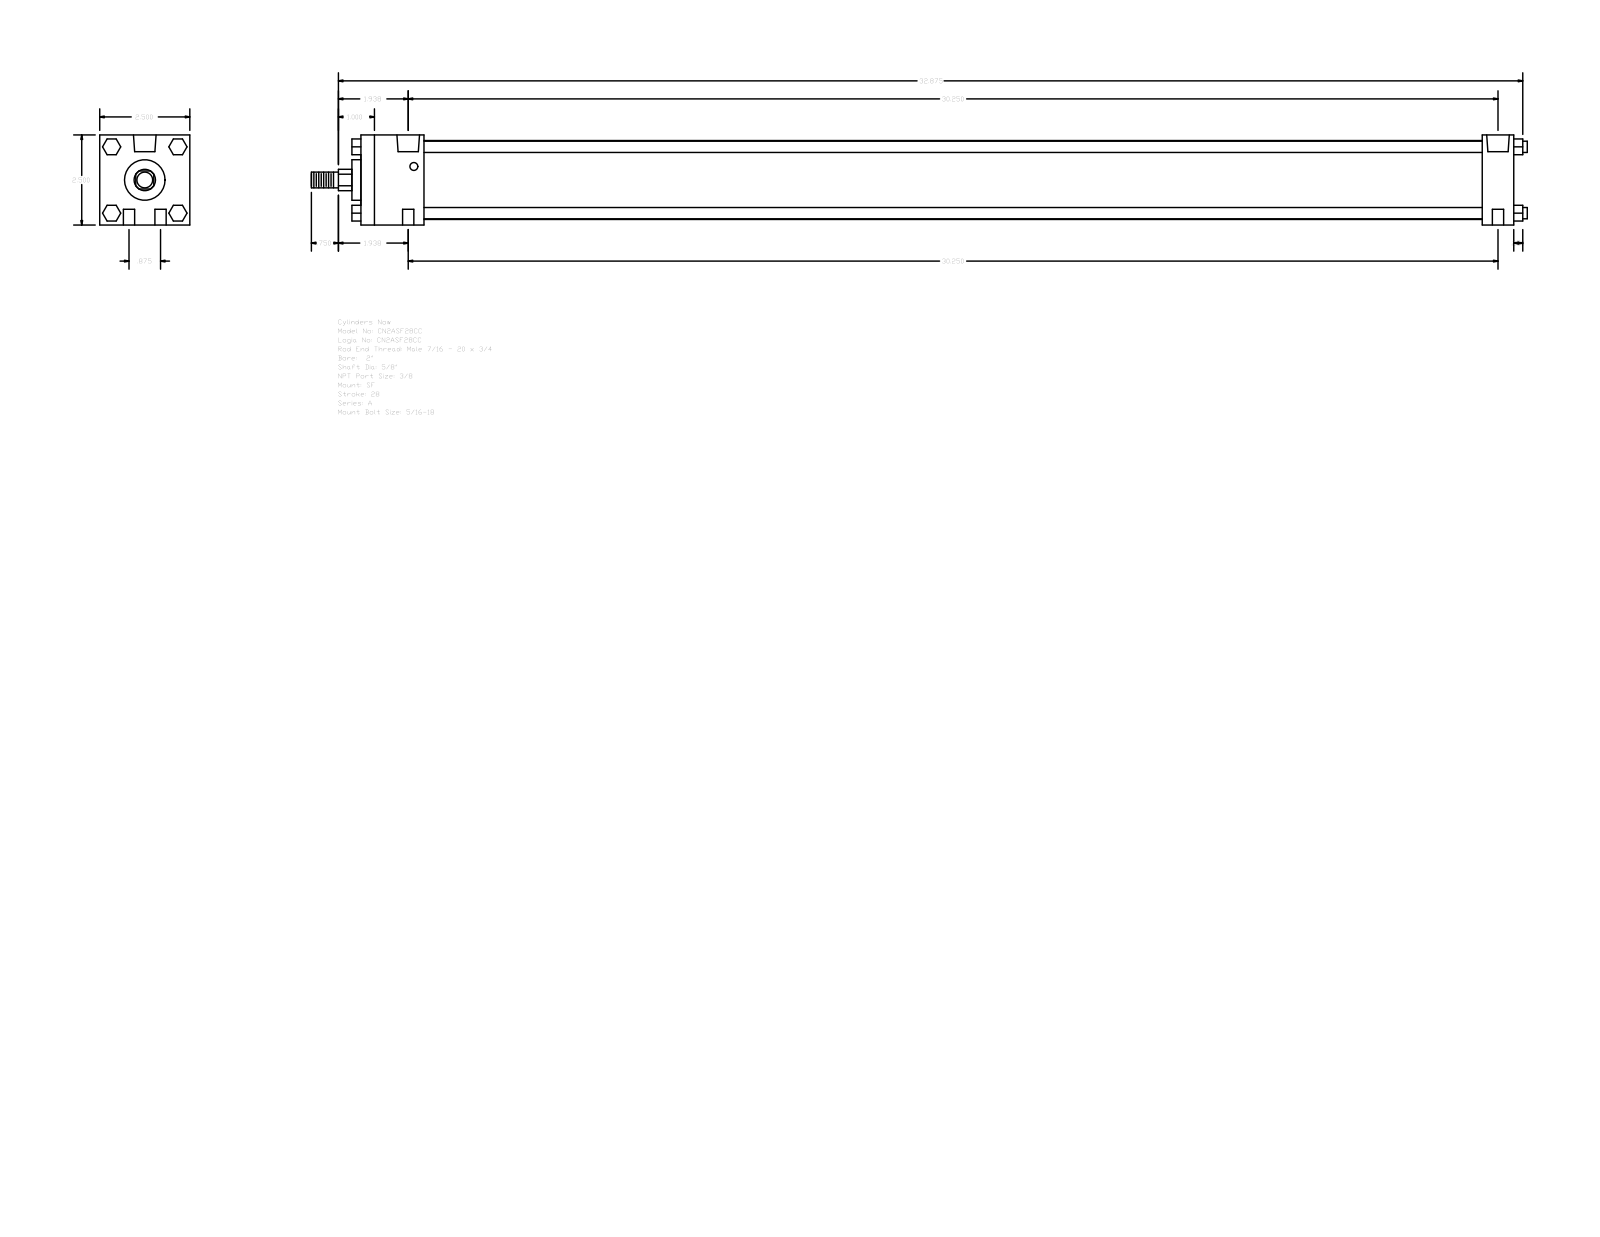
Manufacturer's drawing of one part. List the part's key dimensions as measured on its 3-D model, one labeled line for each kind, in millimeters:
Part name (STEP PRODUCT): A_SF__0200_0.625
STEP written by: GSSL Pune (CONFIG_CONTROL_DESIGN)
Units: millimetres
Bodies: 0 solids, 124 faces (94 planar, 30 cylindrical, 0 other)
Overall size (bounding box): 857.25 × 63.5 × 63.5
Round holes (diameter × count): ⌀7.94 ×4, ⌀5.56 ×2, ⌀15.93 ×2
Round bosses / shafts (diameter × count): ⌀7.94 ×4, ⌀55.63 ×1, ⌀28.57 ×1, ⌀15.88 ×1, ⌀11.11 ×1
Partial cylindrical surfaces — rounded edges, fillets, slot ends (radius × count): R7.54 ×1
Main face-to-face distances: 63.5, 812.79, 790.57, 22.22, 44.45, 746.12, 768.34, 6.35, 819.14, 50.8
Hole centre spacings: 11.11, 768.43, 768.35, 22.22, 768.67, 760.4
